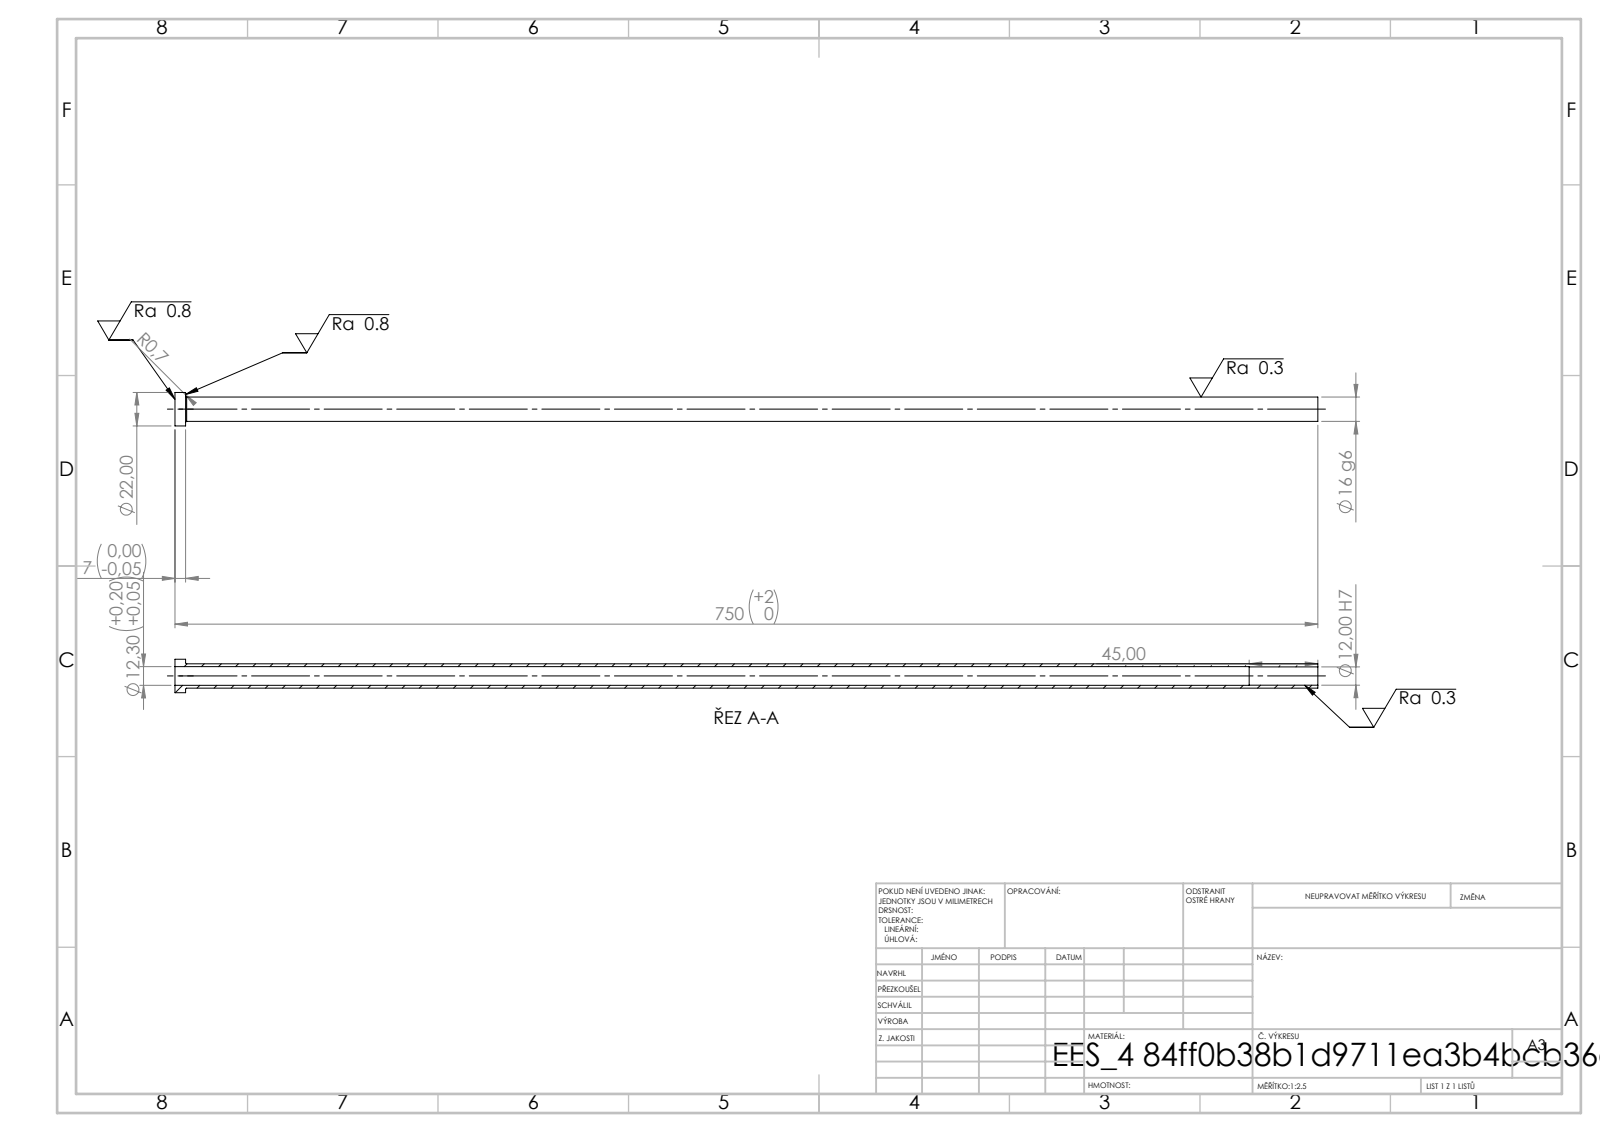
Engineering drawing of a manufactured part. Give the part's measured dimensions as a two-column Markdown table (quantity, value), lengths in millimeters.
| quantity | value |
| --- | --- |
| STEP written by | SolidWorks 2019 (CONFIG_CONTROL_DESIGN) |
| units | millimeters |
| bodies | 1 solid, 14 faces (4 planar, 8 cylindrical, 2 other) |
| overall size | 750 × 22 × 22 |
| volume | 63 196 mm³ |
| surface area | 67 289 mm² |
| round holes (diameter × count) | 12 × 1, 12.3 × 1 |
| round bosses / shafts (diameter × count) | 22 × 1, 16 × 1 |
| main face-to-face distances | 7, 750, 743, 705, 698, 45 |
